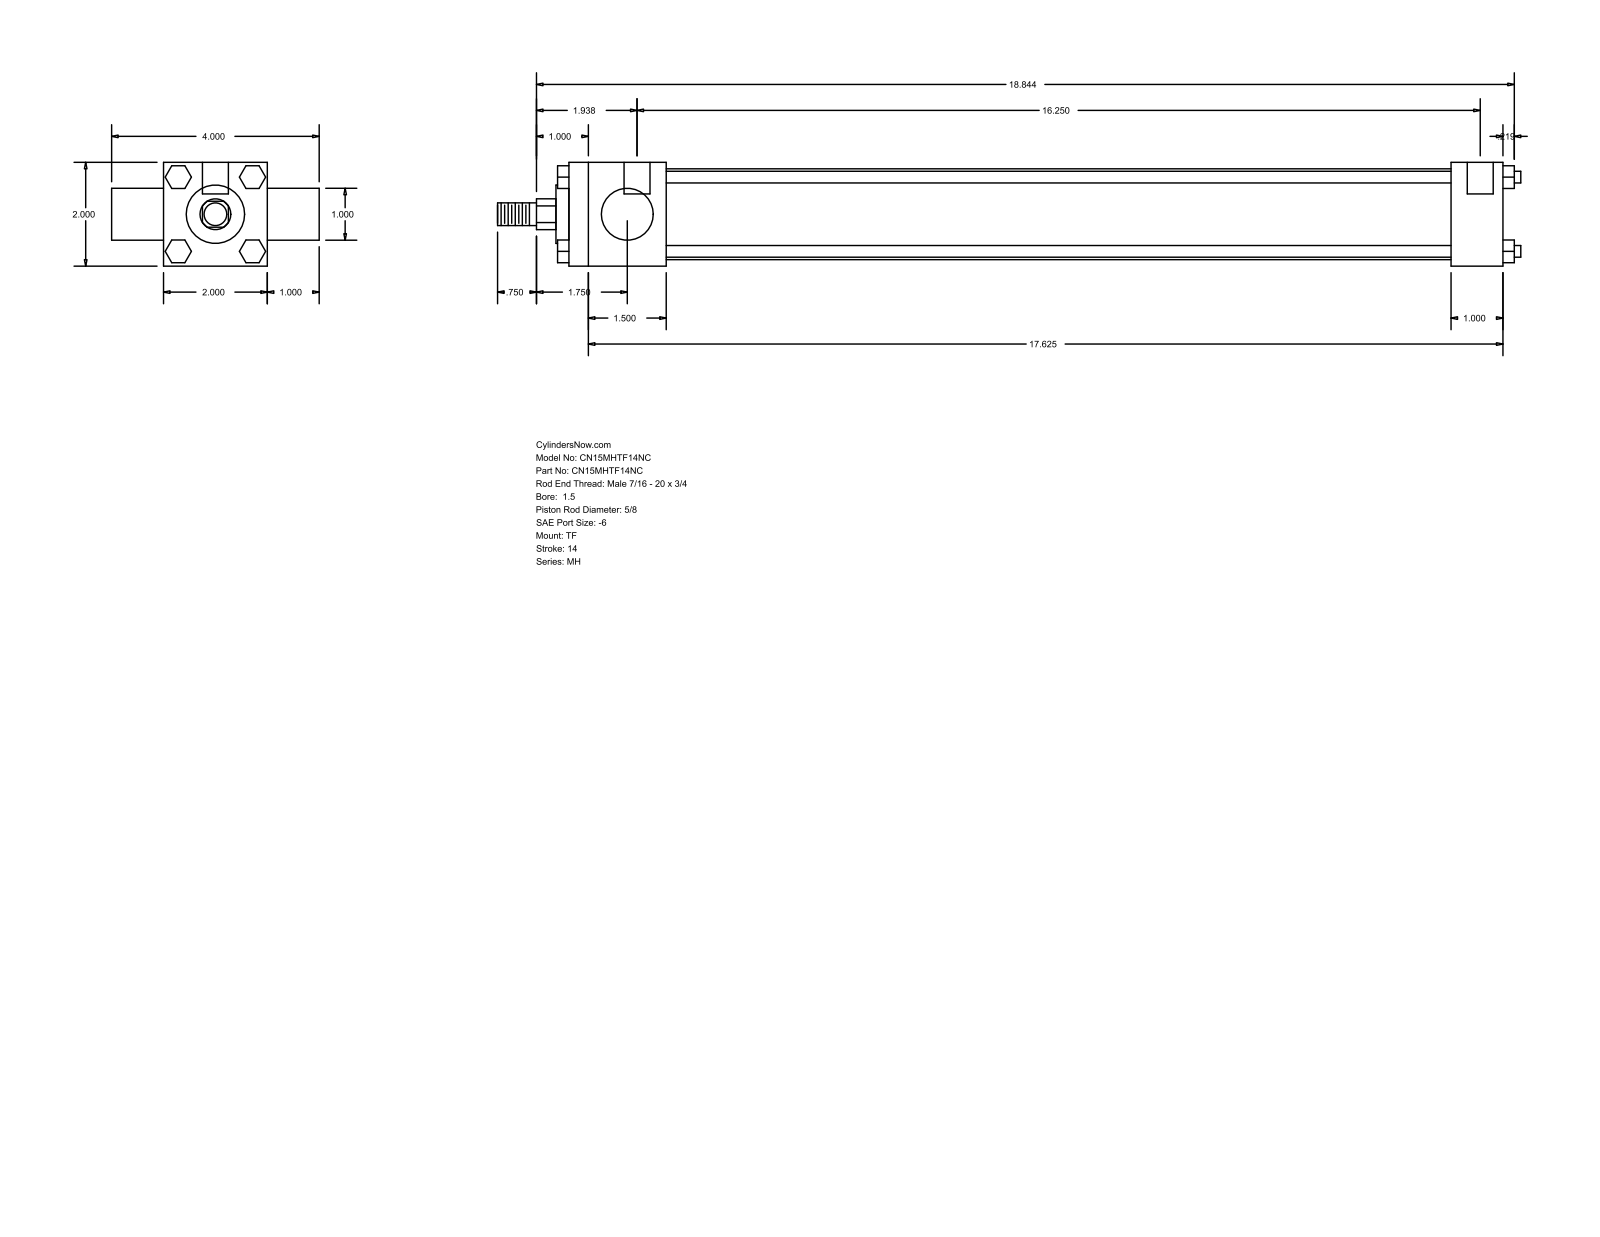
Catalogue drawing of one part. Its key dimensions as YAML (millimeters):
part_name: "MH_TF__0150_0.625"
step_written_by: "GSSL Pune (CONFIG_CONTROL_DESIGN)"
units: millimeters
bodies: {solids: 0, faces: 120, planar: 92, cylindrical: 28, other: 0}
overall_size: [500.86, 101.6, 50.8]
round_holes:
  - {diameter: 5.56, count: 3}
  - {diameter: 12.7, count: 2}
round_bosses_or_shafts:
  - {diameter: 5.71, count: 4}
  - {diameter: 44.45, count: 1}
  - {diameter: 28.57, count: 1}
  - {diameter: 25.4, count: 1}
  - {diameter: 15.88, count: 1}
  - {diameter: 11.11, count: 1}
partial_cylinders:
  - {radius: 7.54, count: 1}
face_to_face_distances: [50.8, 457.19, 25.4, 76.2, 47.62, 409.57, 431.8, 384.18, 25.39, 5.56]
hole_center_spacings: [3.17, 412.75, 415.92]
